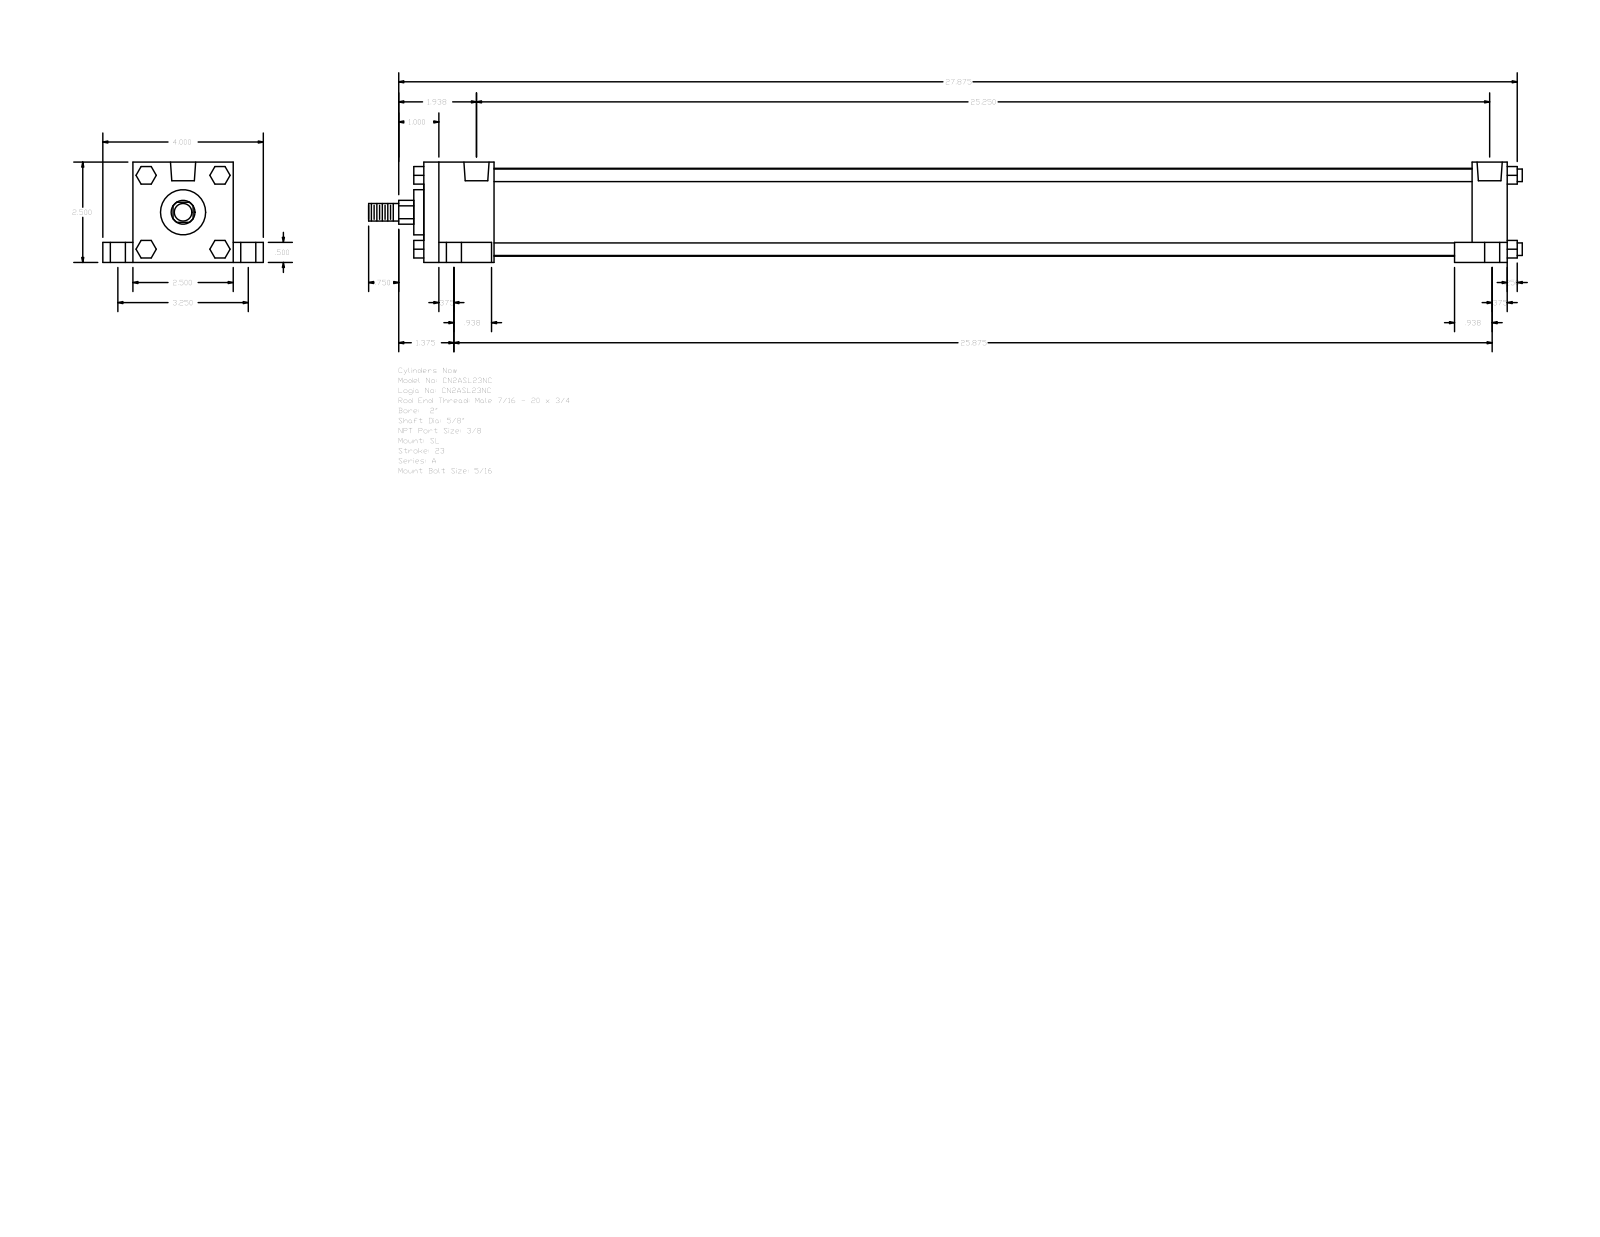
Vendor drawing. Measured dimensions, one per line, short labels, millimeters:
name: A_SL__0200_0.625
written by: GSSL Pune (CONFIG_CONTROL_DESIGN)
unit: mm
bodies: 0 solids, 148 faces (112 planar, 36 cylindrical, 0 other)
size: 730.25 × 101.6 × 63.5
holes: 4× ⌀5.56, 4× ⌀9.53, 4× ⌀15.88, 2× ⌀15.93
bosses: 4× ⌀7.94, 1× ⌀55.63, 1× ⌀28.57, 1× ⌀15.88, 1× ⌀11.11
rounds: 1× R7.54
face distances: 63.5, 685.79, 50.8, 12.7, 19.05, 82.55, 44.45, 641.34, 663.57, 619.12
hole spacings: 41.3, 41.64, 43.67, 45.13, 82.54, 633.4, 640.29, 644.26
